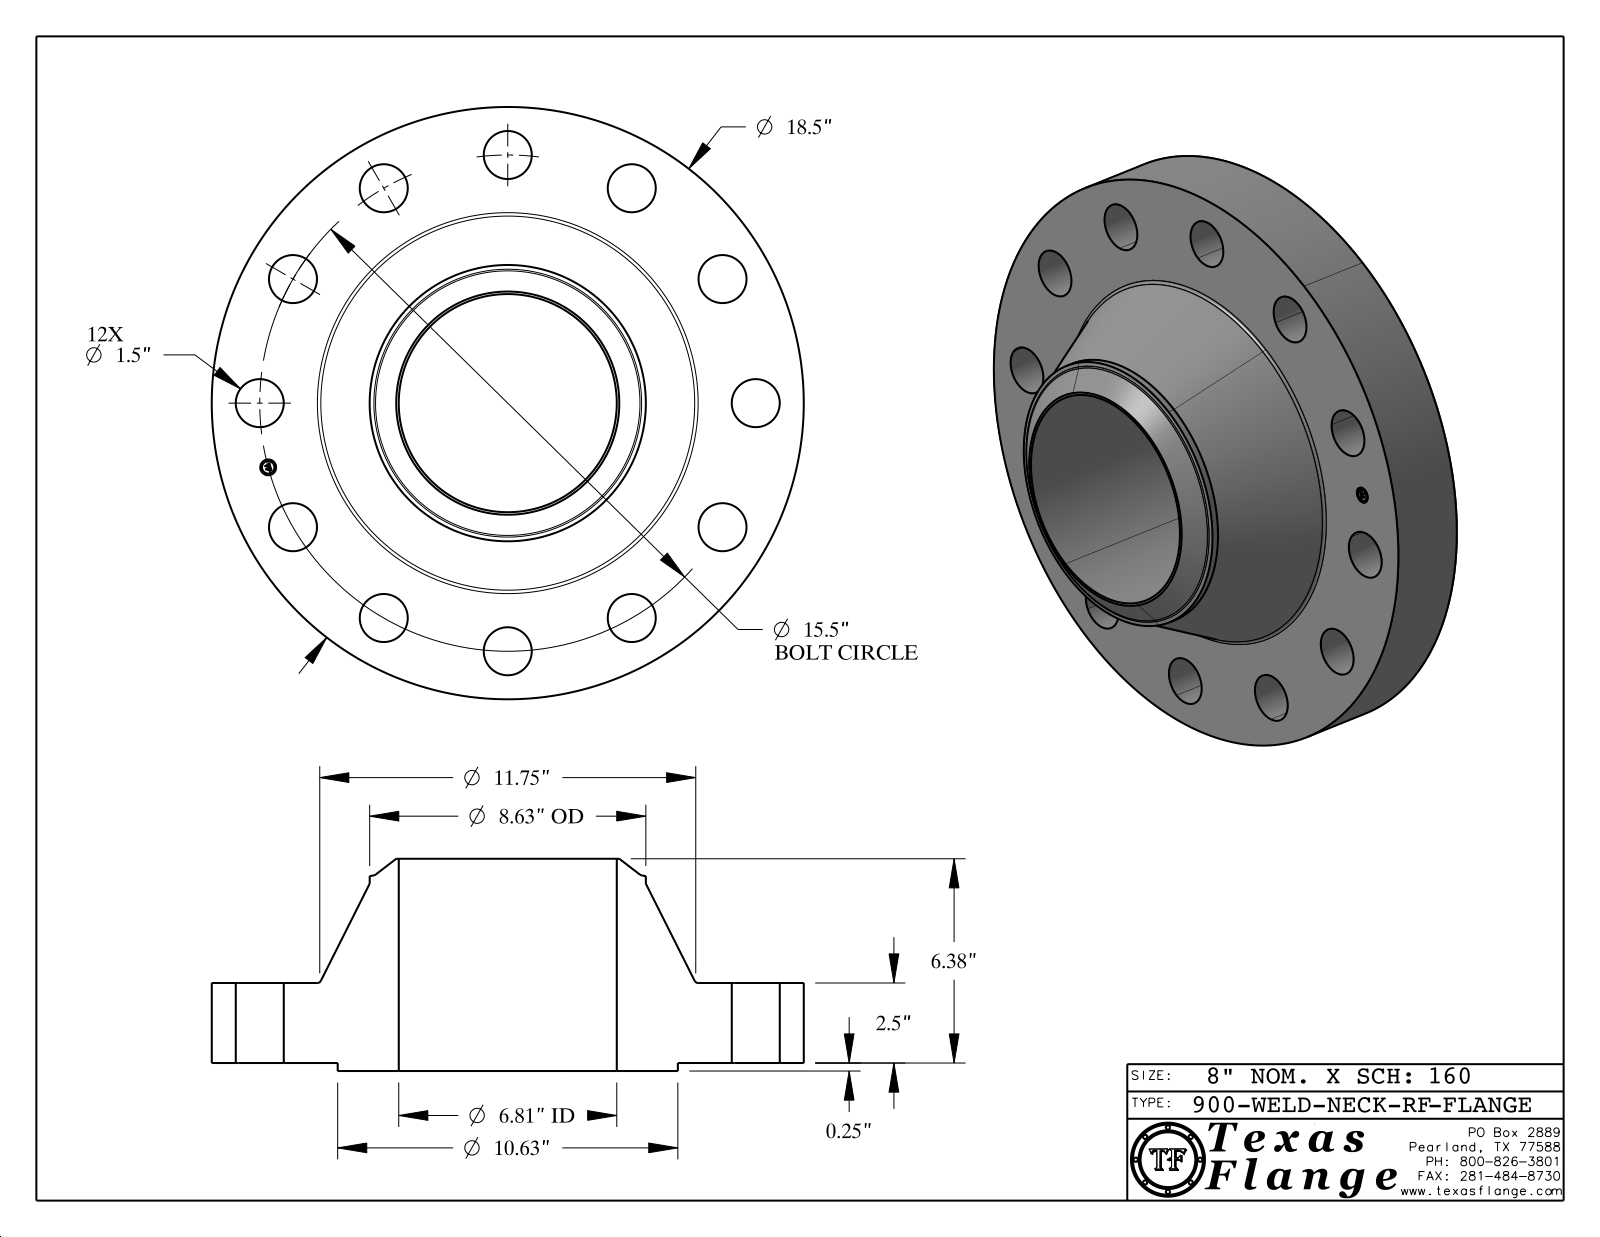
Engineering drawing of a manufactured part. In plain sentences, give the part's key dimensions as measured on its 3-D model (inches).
The part is named "900-WELD-NECK-RF". Its 3-D file was written by "CATIA V5 STEP AP214 (AUTOMOTIVE_DESIGN)". It is 1 solid with 431 faces: 369 planar, 52 cylindrical and 10 other. Overall it measures 18.5 by 18.5 by 6.63 inches. Its volume is 693.5 cubic inches and its surface area 930.6 square inches. Round holes: 12 of diameter 1.5, 1 of diameter 0.495, 1 of diameter 6.813. Round bosses or shafts: 8 of diameter 0.03, 1 of diameter 18.5, 1 of diameter 10.63, 1 of diameter 8.63, 1 of diameter 0.39. The main face-to-face distances are 2.5, 0.25, 2.75, 6.63, 6.38, 3.88, 0.015, 2.735, 2.485, 3.895. The hole center spacings are 7.75, 7.75, 13.424, 4.012, 10.961, 14.972, 4.011, 10.96.
